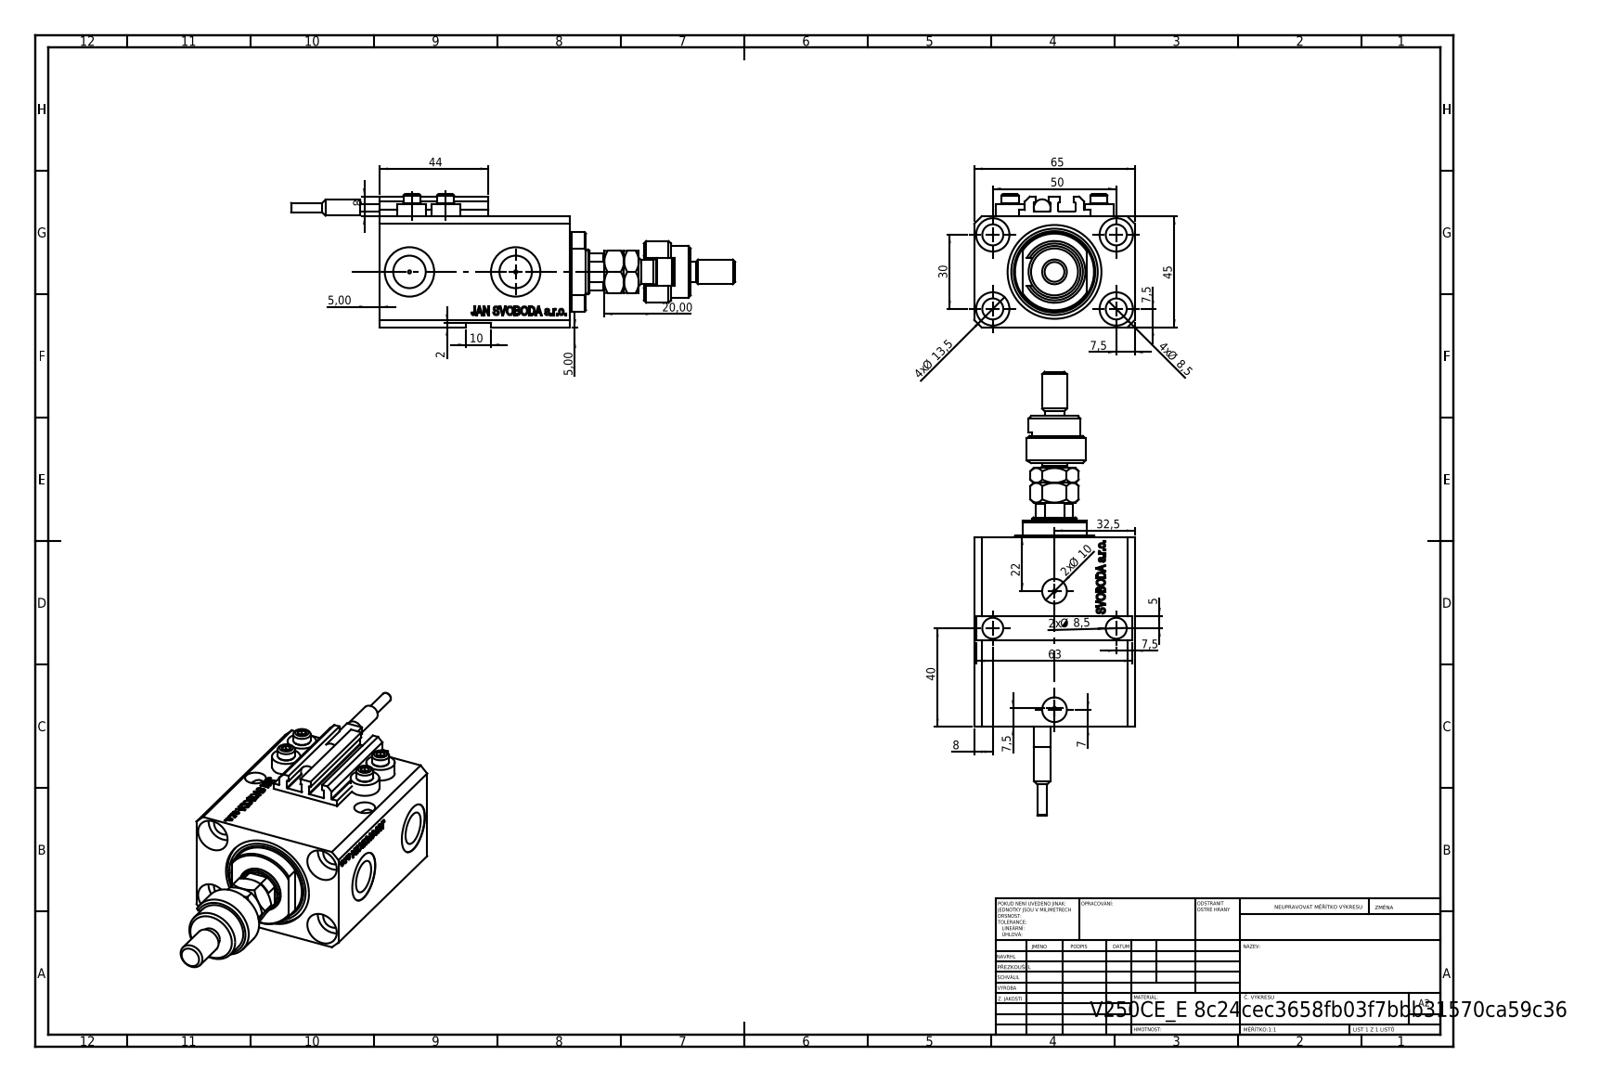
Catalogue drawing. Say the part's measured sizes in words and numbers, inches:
The part is named "SWITCH_V250CE; ALLEN BOLT V250CE; V250CE_E; FEMALE_PART_FOR_DFA (+3 more)". Its 3-D file was written by "SolidWorks 2019 (CONFIG_CONTROL_DESIGN)". It is 11 solids with 1194 faces: 559 planar, 157 cylindrical and 478 other. Overall it measures 7.083 by 2.559 by 2.126 inches. Its volume is 12.8 cubic inches and its surface area 107.3 square inches. Round holes: 7 of diameter 0.335, 4 of diameter 0.049, 4 of diameter 0.157, 4 of diameter 0.531, 2 of diameter 0.394, 2 of diameter 0.518, 2 of diameter 0.787, 1 of diameter 0.709, 1 of diameter 1.496. Round bosses or shafts: 4 of diameter 0.457, 4 of diameter 0.276, 1 of diameter 0.984, 1 of diameter 0.827, 1 of diameter 0.63, 1 of diameter 0.394, 1 of diameter 0.315, 1 of diameter 0.268. Partial cylindrical surfaces (rounded edges, fillets, slot ends): 10 of radius 0.008, 1 of radius 0.217, 1 of radius 0.335, 1 of radius 0.344, 1 of radius 0.63. The main face-to-face distances are 1.772, 2.559, 2.043, 0.079, 3.031, 0.988, 0.118, 0.272, 2.76, 1.85. The hole center spacings are 1.148, 1.969, 0.535, 0.595, 0.741, 0.747, 1.032, 1.048.
